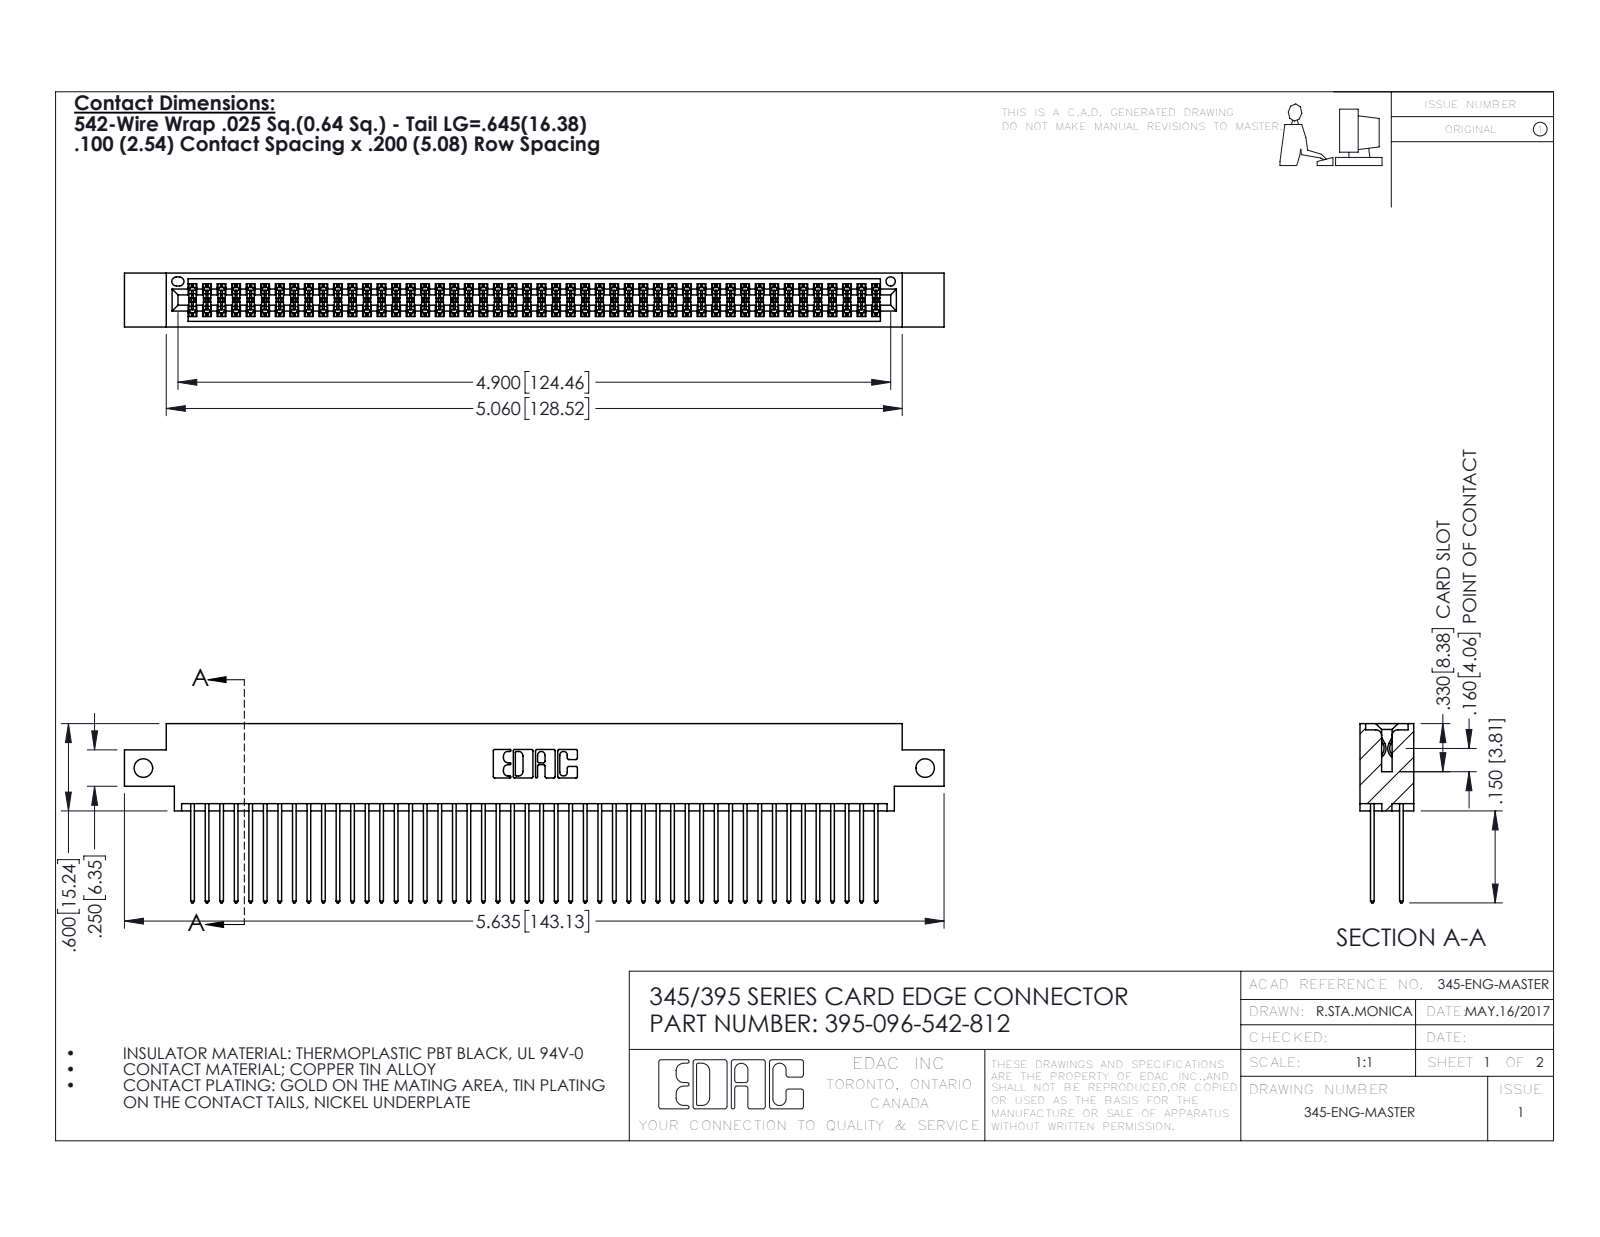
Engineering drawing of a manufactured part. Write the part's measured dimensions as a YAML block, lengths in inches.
part_name: "395-096-542-812; 345 Part_0.170 Offset - Side Mount; 345-292-001_345-293-142"
step_written_by: "SolidWorks 2016 (CONFIG_CONTROL_DESIGN)"
units: inches
bodies: {solids: 97, faces: 4930, planar: 3252, cylindrical: 1678, other: 0}
overall_size: [5.635, 1.232, 0.37]
volume: 0.867
surface_area: 35.98
round_holes:
  - {diameter: 0.128, count: 2}
  - {diameter: 0.064, count: 1}
partial_cylinders:
  - {radius: 0.006, count: 144}
  - {radius: 0.01, count: 96}
  - {radius: 0.01, count: 22}
  - {radius: 0.007, count: 6}
  - {radius: 0.031, count: 6}
  - {radius: 0.026, count: 3}
  - {radius: 0.014, count: 2}
  - {radius: 0.019, count: 2}
face_to_face_distances: [0.072, 0.298, 0.2, 0.098, 0.272, 0.025, 0.37, 0.225, 0.175, 0.149]
hole_center_spacings: [5.375]
